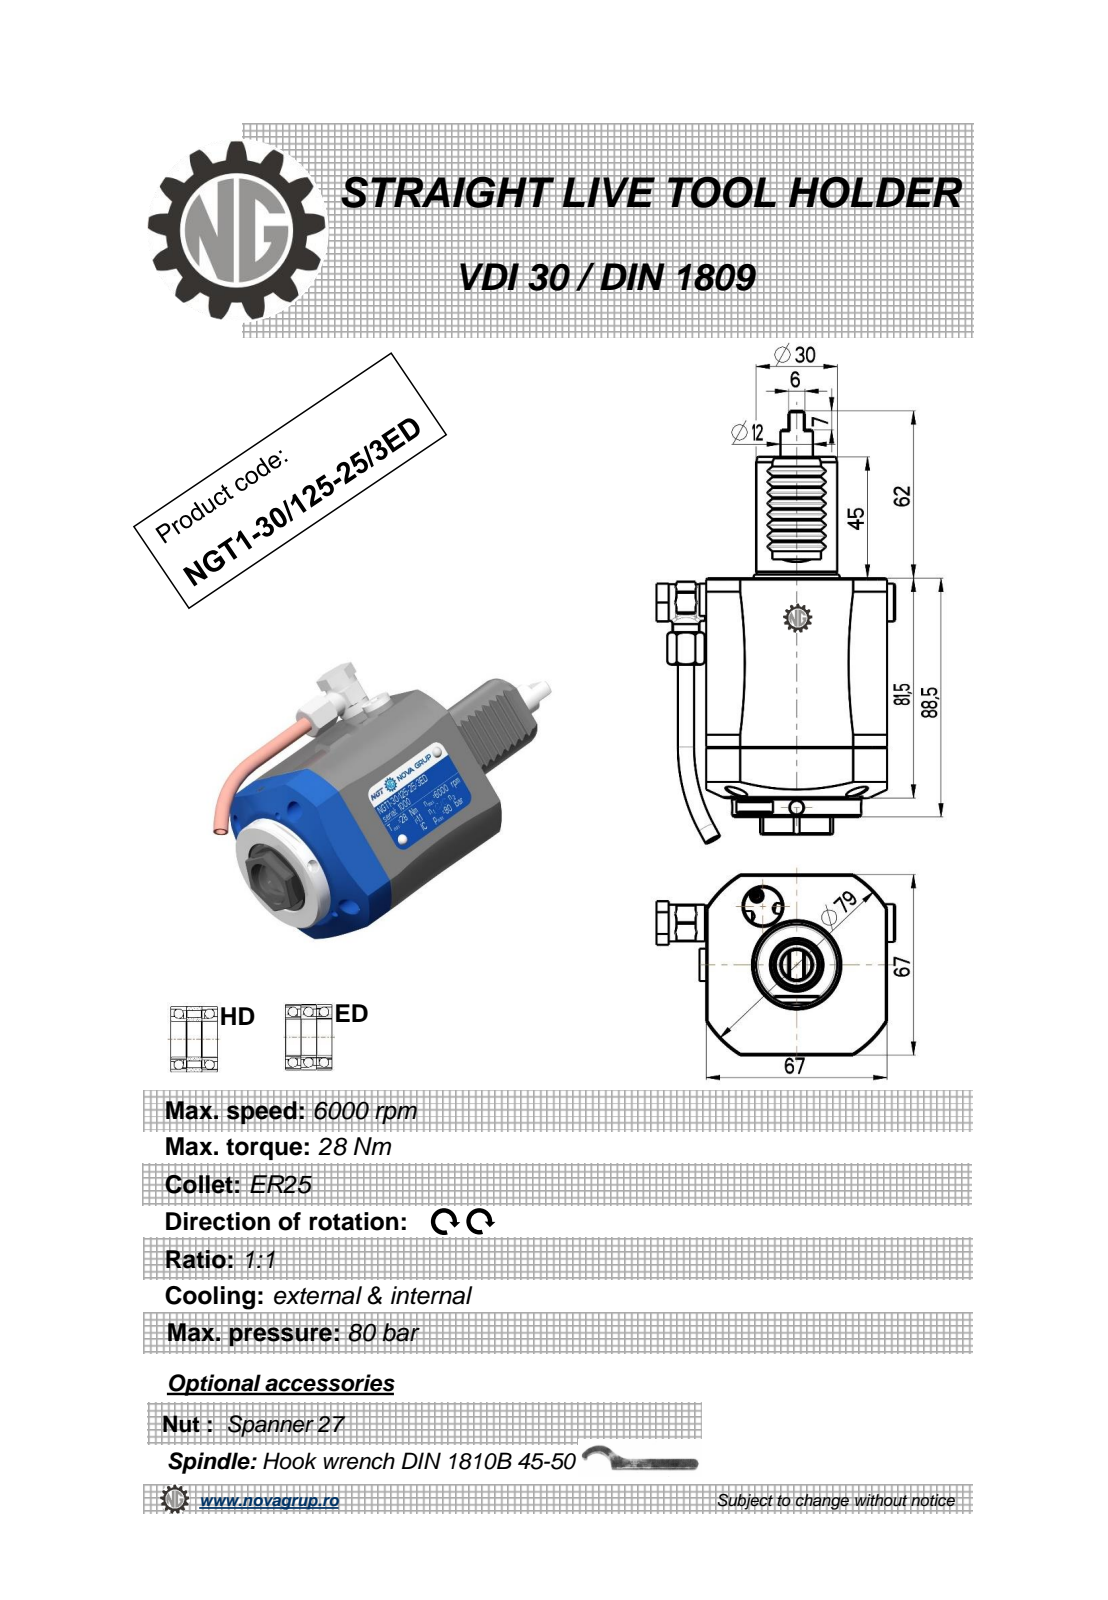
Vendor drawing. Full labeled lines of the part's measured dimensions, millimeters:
Part name (STEP PRODUCT): NGT1_30_125_25_3HD
STEP written by: PRO/ENGINEER BY PARAMETRIC TECHNOLOGY CORPORATION, 2010280 (CONFIG_CONTROL_DESIGN)
Units: millimetres
Bodies: 2 solids, 357 faces (141 planar, 101 cylindrical, 115 other)
Overall size (bounding box): 160.33 × 88.4 × 67
Volume: 384 497 mm³ · Surface area: 40 936 mm²
Round holes (diameter × count): ⌀4 ×3, ⌀5 ×2, ⌀3 ×1, ⌀6 ×1, ⌀6.2 ×1, ⌀9 ×1, ⌀10 ×1, ⌀11 ×1, ⌀18 ×1, ⌀26.5 ×1
Round bosses / shafts (diameter × count): ⌀12 ×2, ⌀48 ×1, ⌀30 ×1, ⌀14 ×1, ⌀13.6 ×1, ⌀13 ×1, ⌀10 ×1, ⌀8.5 ×1
Partial cylindrical surfaces — rounded edges, fillets, slot ends (radius × count): R0.3 ×8, R0.41 ×6, R0.5 ×4, R0.8 ×2, R7.7 ×1, R39.5 ×1
Main face-to-face distances: 67, 88.5, 7, 81.5, 2.83, 133.5, 126.5, 45, 12, 6.5
Hole centre spacings: 0.4, 43.83, 44.21, 77.56
